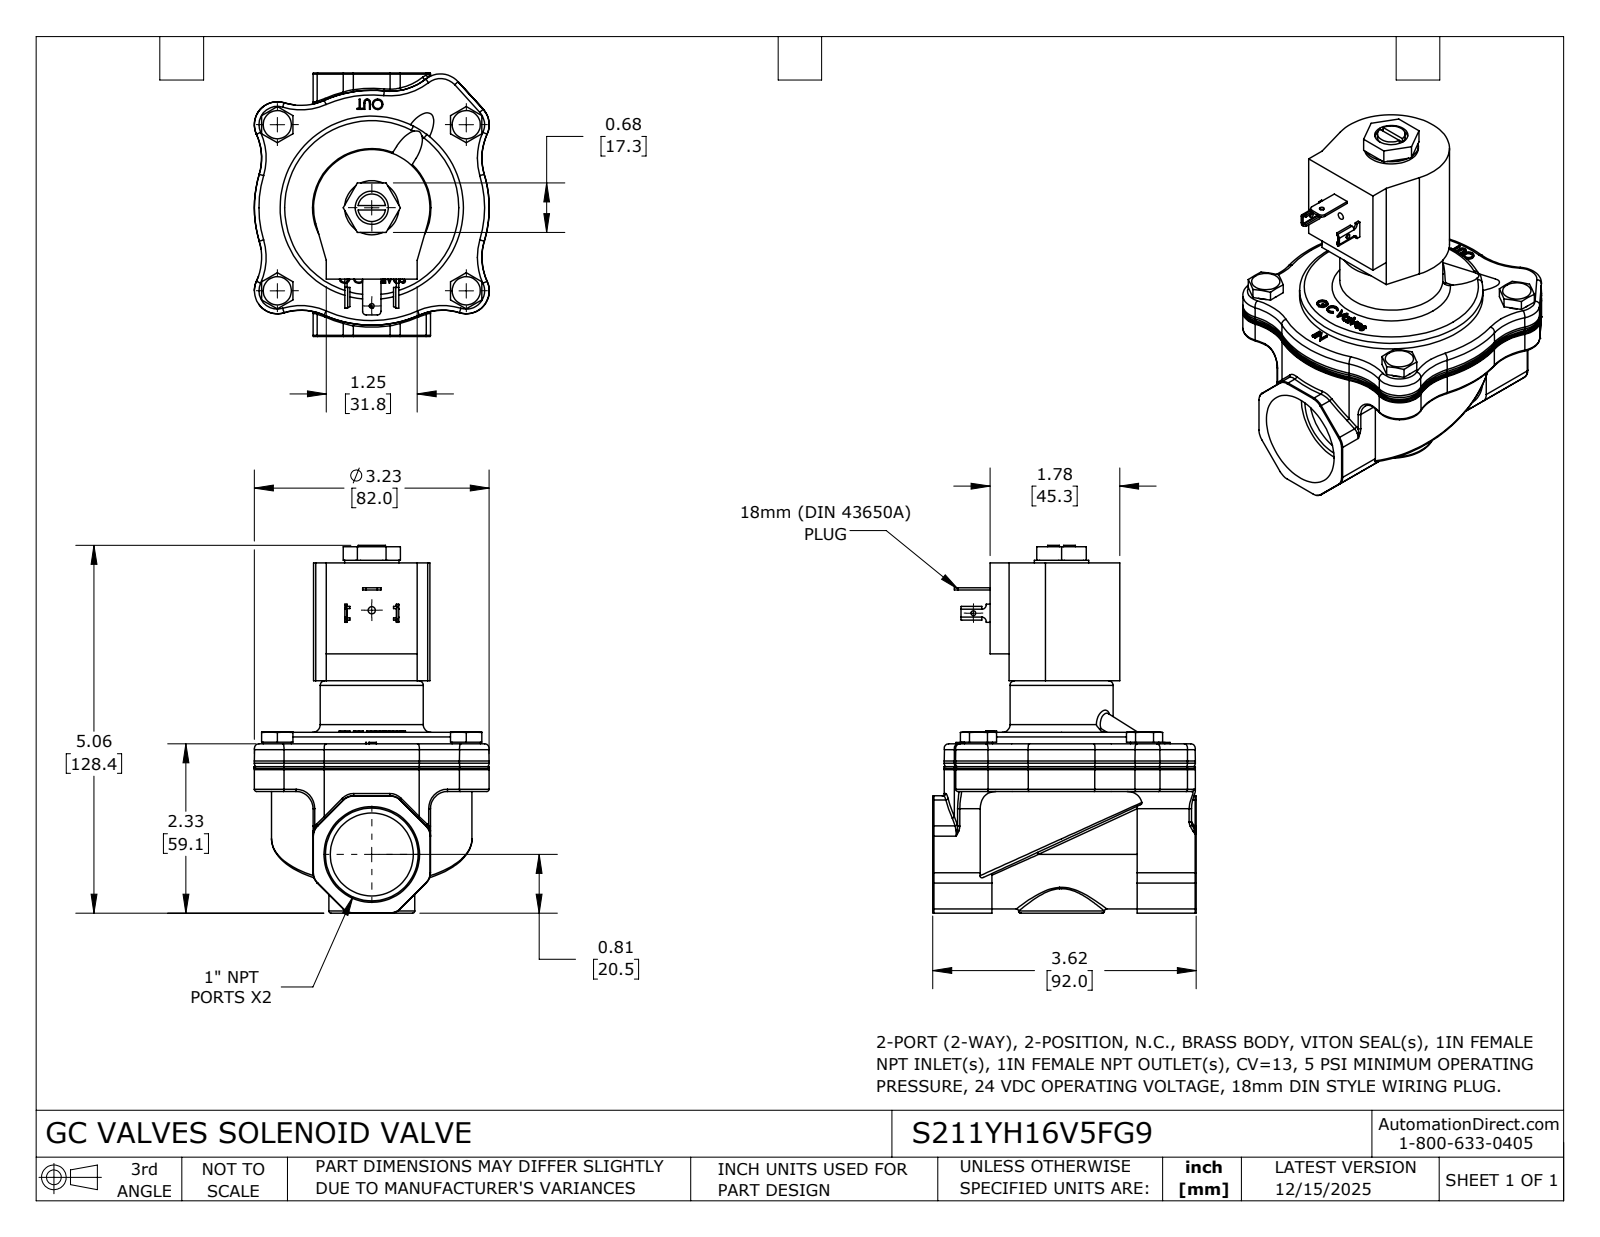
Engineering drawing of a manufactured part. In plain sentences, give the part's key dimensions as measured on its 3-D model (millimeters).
The part is named "S211YH16V5FG9". Its 3-D file was written by "SolidWorks 2024 (CONFIG_CONTROL_DESIGN)". It is 1 solid with 671 faces: 220 planar, 172 cylindrical and 279 other. Overall it measures 128.4 by 92 by 82.1 millimeters. Its volume is 322 300 cubic millimeters and its surface area 44 200 square millimeters. Round holes: 1 of diameter 1.7, 1 of diameter 1.7, 1 of diameter 2.5, 1 of diameter 11.6, 1 of diameter 29. Round bosses or shafts: 4 of diameter 9.9, 1 of diameter 64, 1 of diameter 36, 1 of diameter 30, 1 of diameter 18.9, 1 of diameter 9.7. Partial cylindrical surfaces (rounded edges, fillets, slot ends): 24 of radius 0.8, 24 of radius 20, 12 of radius 8, 8 of radius 5, 4 of radius 0.2, 4 of radius 1, 2 of radius 1.3, 2 of radius 1.5. The main face-to-face distances are 4, 16.6, 20.6, 79.8, 63.1, 59.2, 63.1, 59.1, 42.5, 122.3. The hole center spacings are 34.3, 85.2.
